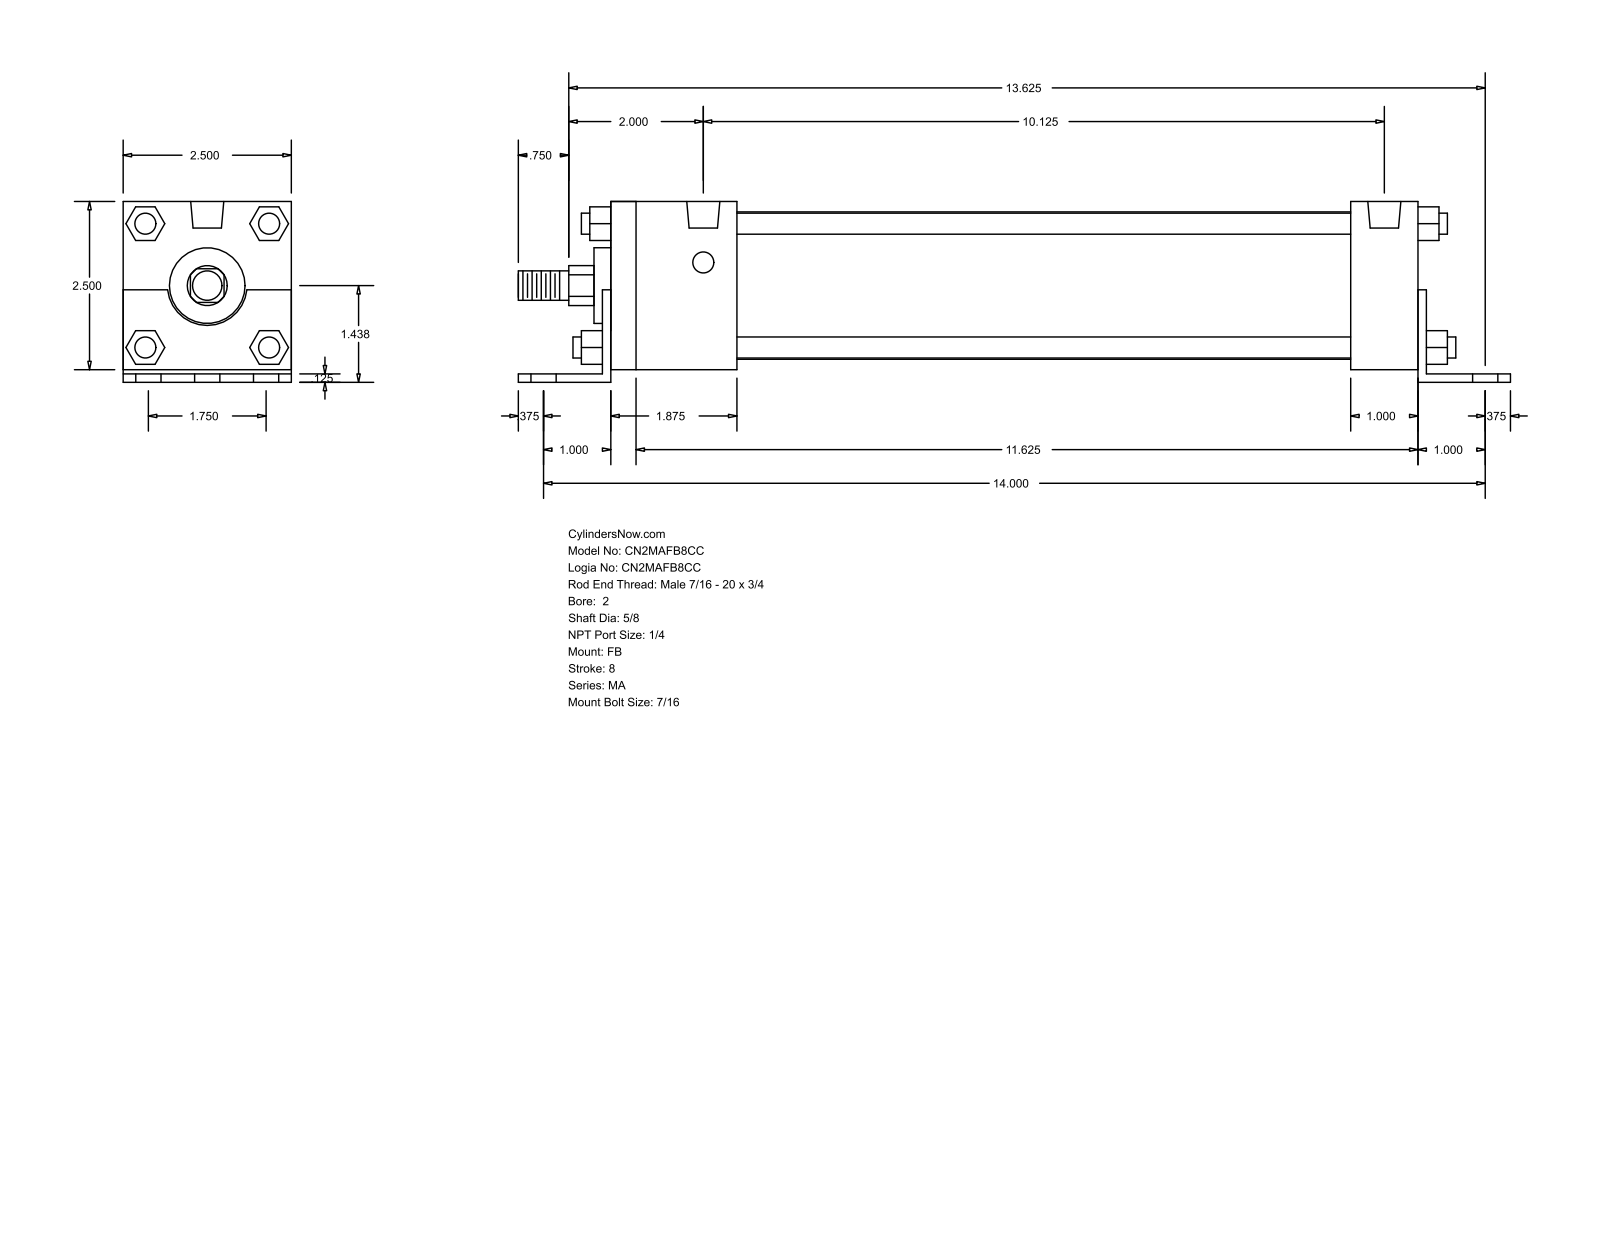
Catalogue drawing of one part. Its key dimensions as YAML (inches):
part_name: "MA_FB__0200_0.625"
step_written_by: "GSSL Pune (CONFIG_CONTROL_DESIGN)"
units: inches
bodies: {solids: 0, faces: 140, planar: 105, cylindrical: 35, other: 0}
overall_size: [14.75, 2.687, 2.5]
round_holes:
  - {diameter: 0.437, count: 6}
  - {diameter: 0.313, count: 4}
  - {diameter: 0.492, count: 2}
round_bosses_or_shafts:
  - {diameter: 0.313, count: 4}
  - {diameter: 2.19, count: 1}
  - {diameter: 1.125, count: 1}
  - {diameter: 0.625, count: 1}
  - {diameter: 0.437, count: 1}
partial_cylinders:
  - {radius: 0.297, count: 1}
  - {radius: 0.593, count: 1}
face_to_face_distances: [2.5, 0.125, 0.187, 2.687, 0.063, 2.563, 12.25, 0.125, 12, 12.125]
hole_center_spacings: [0.875, 14.027, 14, 1.736, 1.75, 2.531, 10.125, 11.658]
